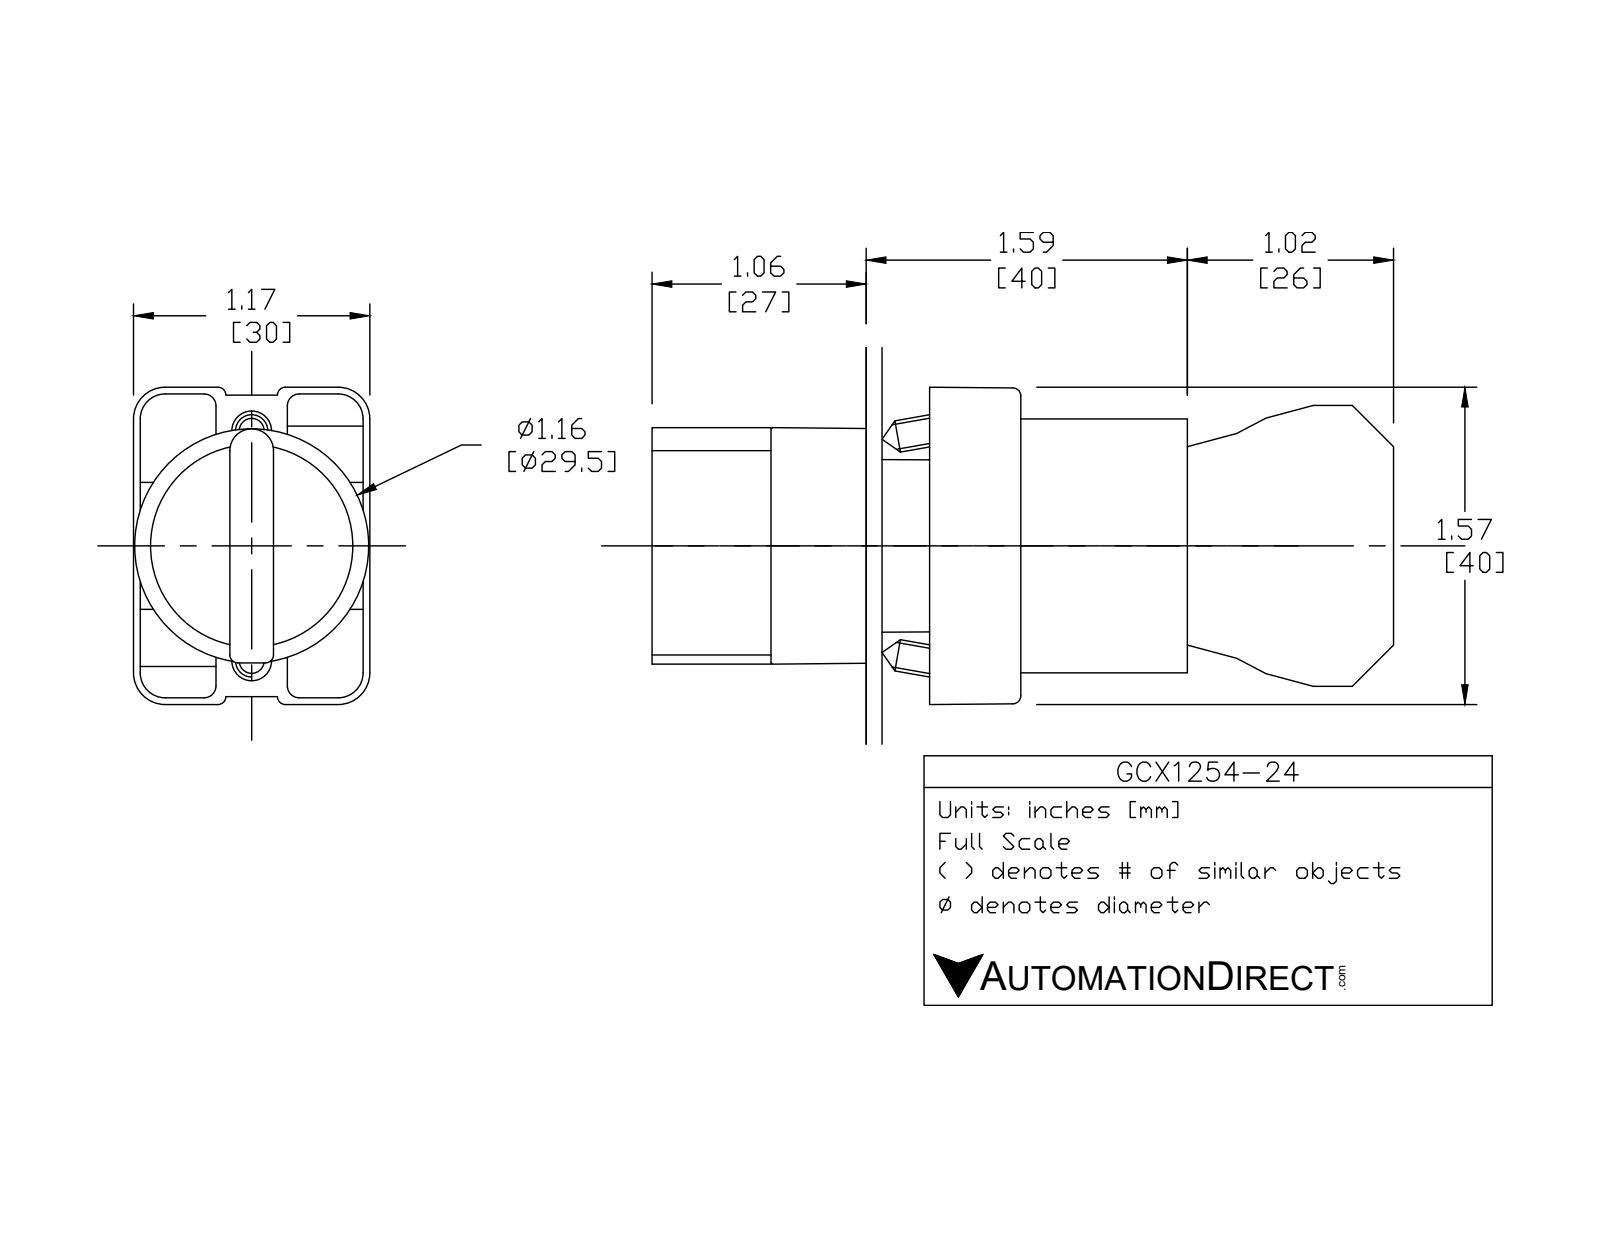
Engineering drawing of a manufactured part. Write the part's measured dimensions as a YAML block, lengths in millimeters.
part_name: "GCX1254-24; ecx1029; ecx1040; GCX1254 OPERATOR (+1 more)"
step_written_by: "SolidWorks 2016 (AUTOMOTIVE_DESIGN)"
units: millimeters
bodies: {solids: 8, faces: 445, planar: 263, cylindrical: 151, other: 31}
overall_size: [92.8, 40.2, 29.9]
volume: 45870
surface_area: 25160
round_holes:
  - {diameter: 2, count: 2}
  - {diameter: 3.1, count: 2}
  - {diameter: 3.3, count: 2}
  - {diameter: 2.2, count: 1}
  - {diameter: 5, count: 1}
  - {diameter: 11.9, count: 1}
  - {diameter: 22.3, count: 1}
  - {diameter: 22.6, count: 1}
  - {diameter: 26, count: 1}
round_bosses_or_shafts:
  - {diameter: 4, count: 4}
  - {diameter: 29.8, count: 1}
  - {diameter: 25.5, count: 1}
  - {diameter: 24, count: 1}
  - {diameter: 21.7, count: 1}
  - {diameter: 19.8, count: 1}
  - {diameter: 12.8, count: 1}
partial_cylinders:
  - {radius: 1.5, count: 24}
  - {radius: 1, count: 12}
  - {radius: 3.1, count: 12}
  - {radius: 4, count: 12}
  - {radius: 1, count: 9}
  - {radius: 3.3, count: 2}
  - {radius: 0.5, count: 1}
  - {radius: 1.6, count: 1}
face_to_face_distances: [21, 51.3, 30.3, 14.7, 31.6, 29.7, 12, 11.9, 0.8, 0.8]
hole_center_spacings: [6, 13.8, 12, 12.4]
